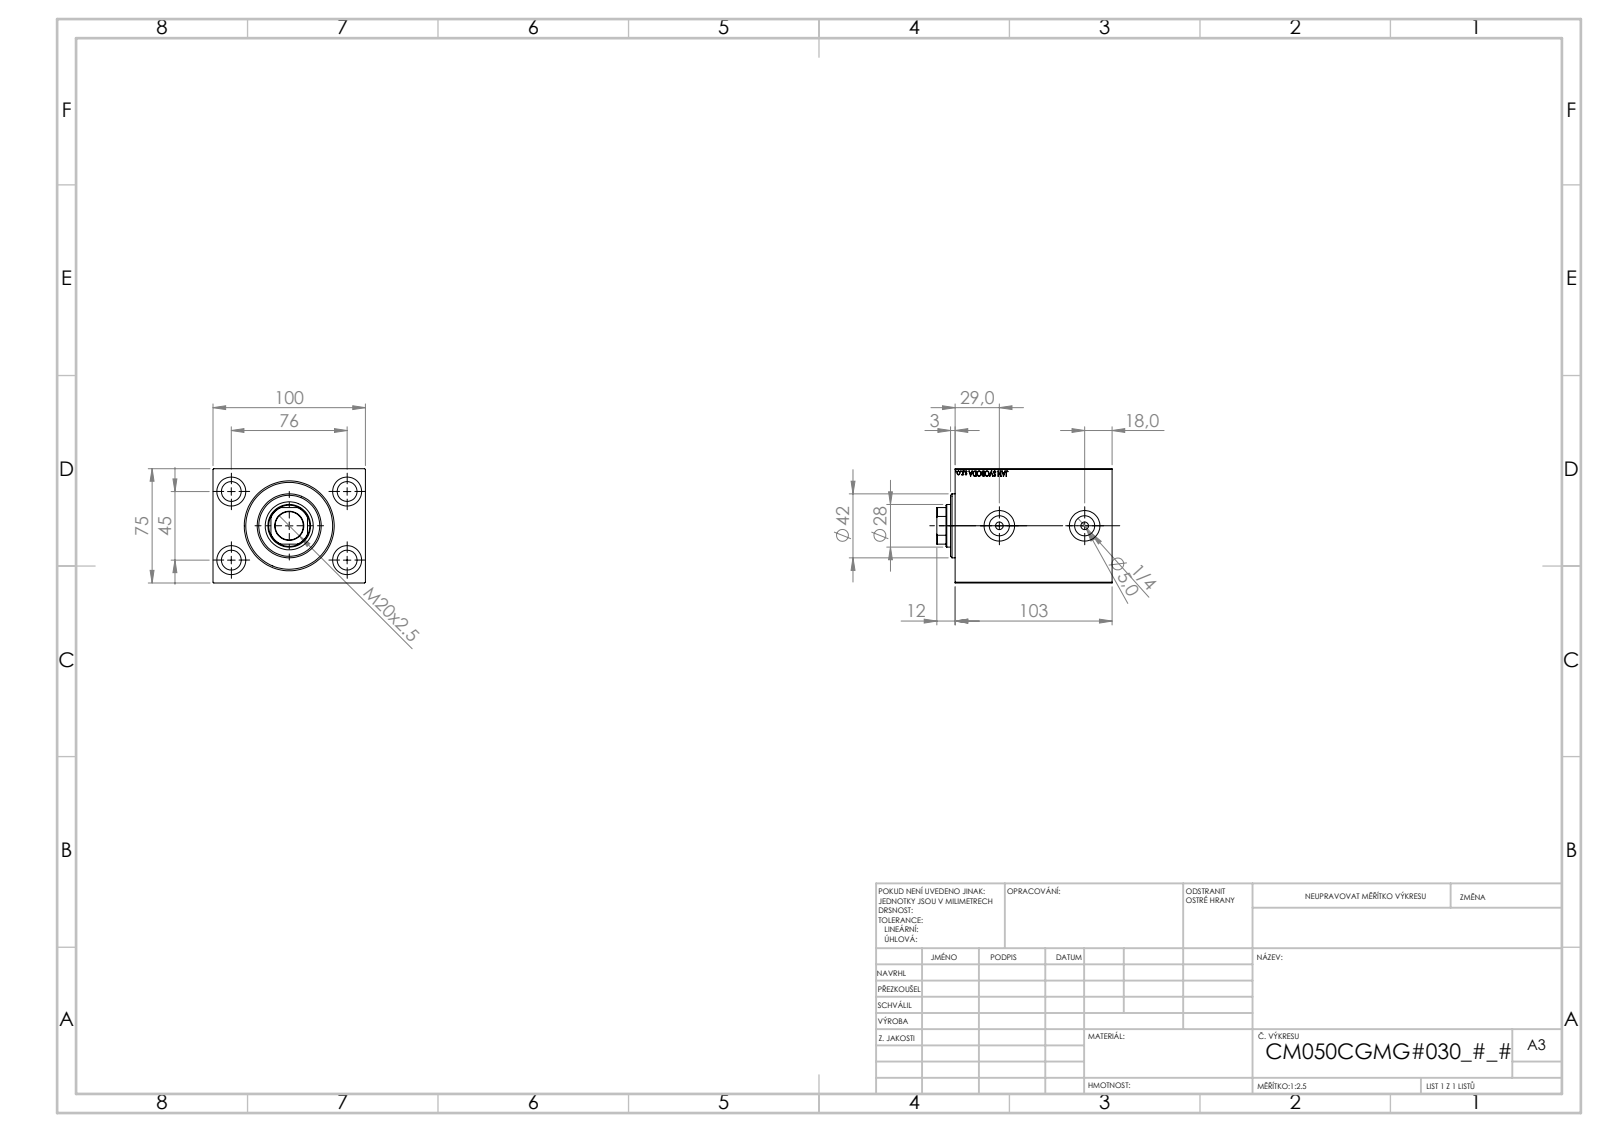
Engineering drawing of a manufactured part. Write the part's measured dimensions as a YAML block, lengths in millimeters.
part_name: "V450CM_C_VCP; V450CM_VC_B; V450CM_C_Body"
step_written_by: "SolidWorks 2019 (CONFIG_CONTROL_DESIGN)"
units: millimeters
bodies: {solids: 3, faces: 865, planar: 409, cylindrical: 62, other: 394}
overall_size: [115, 100, 75]
volume: 659025
surface_area: 109276
round_holes:
  - {diameter: 13, count: 4}
  - {diameter: 19, count: 4}
  - {diameter: 5, count: 2}
  - {diameter: 13.16, count: 2}
  - {diameter: 20, count: 2}
  - {diameter: 18.5, count: 1}
  - {diameter: 28, count: 1}
  - {diameter: 31.5, count: 1}
  - {diameter: 50, count: 1}
  - {diameter: 52, count: 1}
  - {diameter: 57, count: 1}
round_bosses_or_shafts:
  - {diameter: 42, count: 1}
partial_cylinders:
  - {radius: 13.5, count: 1}
face_to_face_distances: [75, 100, 103, 89, 14, 77, 12, 91, 42, 30]
hole_center_spacings: [44.16, 45, 76, 88.32, 56]
